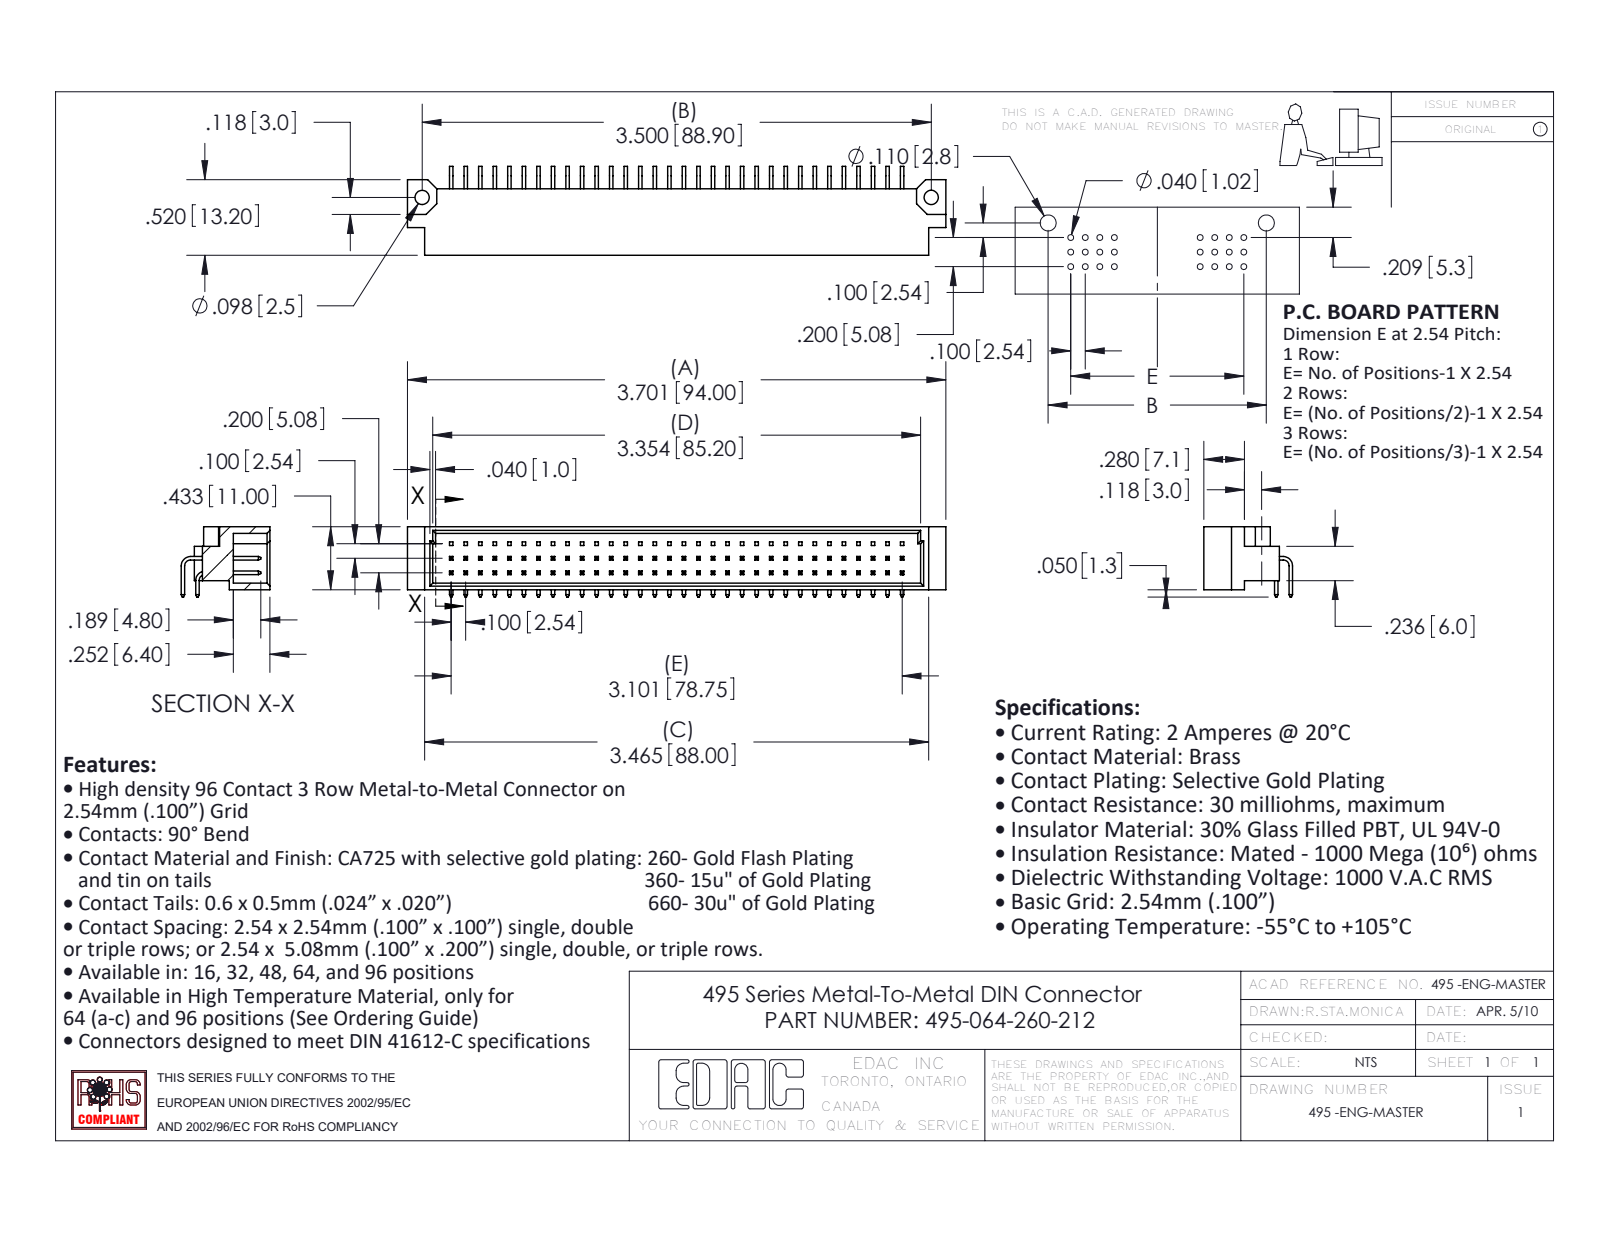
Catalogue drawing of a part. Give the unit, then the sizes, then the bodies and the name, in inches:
Units: inches
Overall size (bounding box): 3.701 × 0.611 × 0.483
Round holes (diameter × count): ⌀0.098 ×2
Partial cylindrical surfaces — rounded edges, fillets, slot ends (radius × count): R0.04 ×2, R0.065 ×2
Main face-to-face distances: 0.1, 0.205, 0.045, 0.388, 0.024, 0.433, 0.343, 0.063, 0.37, 0.124
Hole centre spacings: 3.5
Volume: 0.386 in³ · Surface area: 14.75 in²
Bodies: 65 solids, 1585 faces (1453 planar, 132 cylindrical, 0 other)
Part name (STEP PRODUCT): 495-290-2; 495-290-3; 495 Part_96; 495-064-260-212
STEP written by: SolidWorks 2020 (AUTOMOTIVE_DESIGN)
